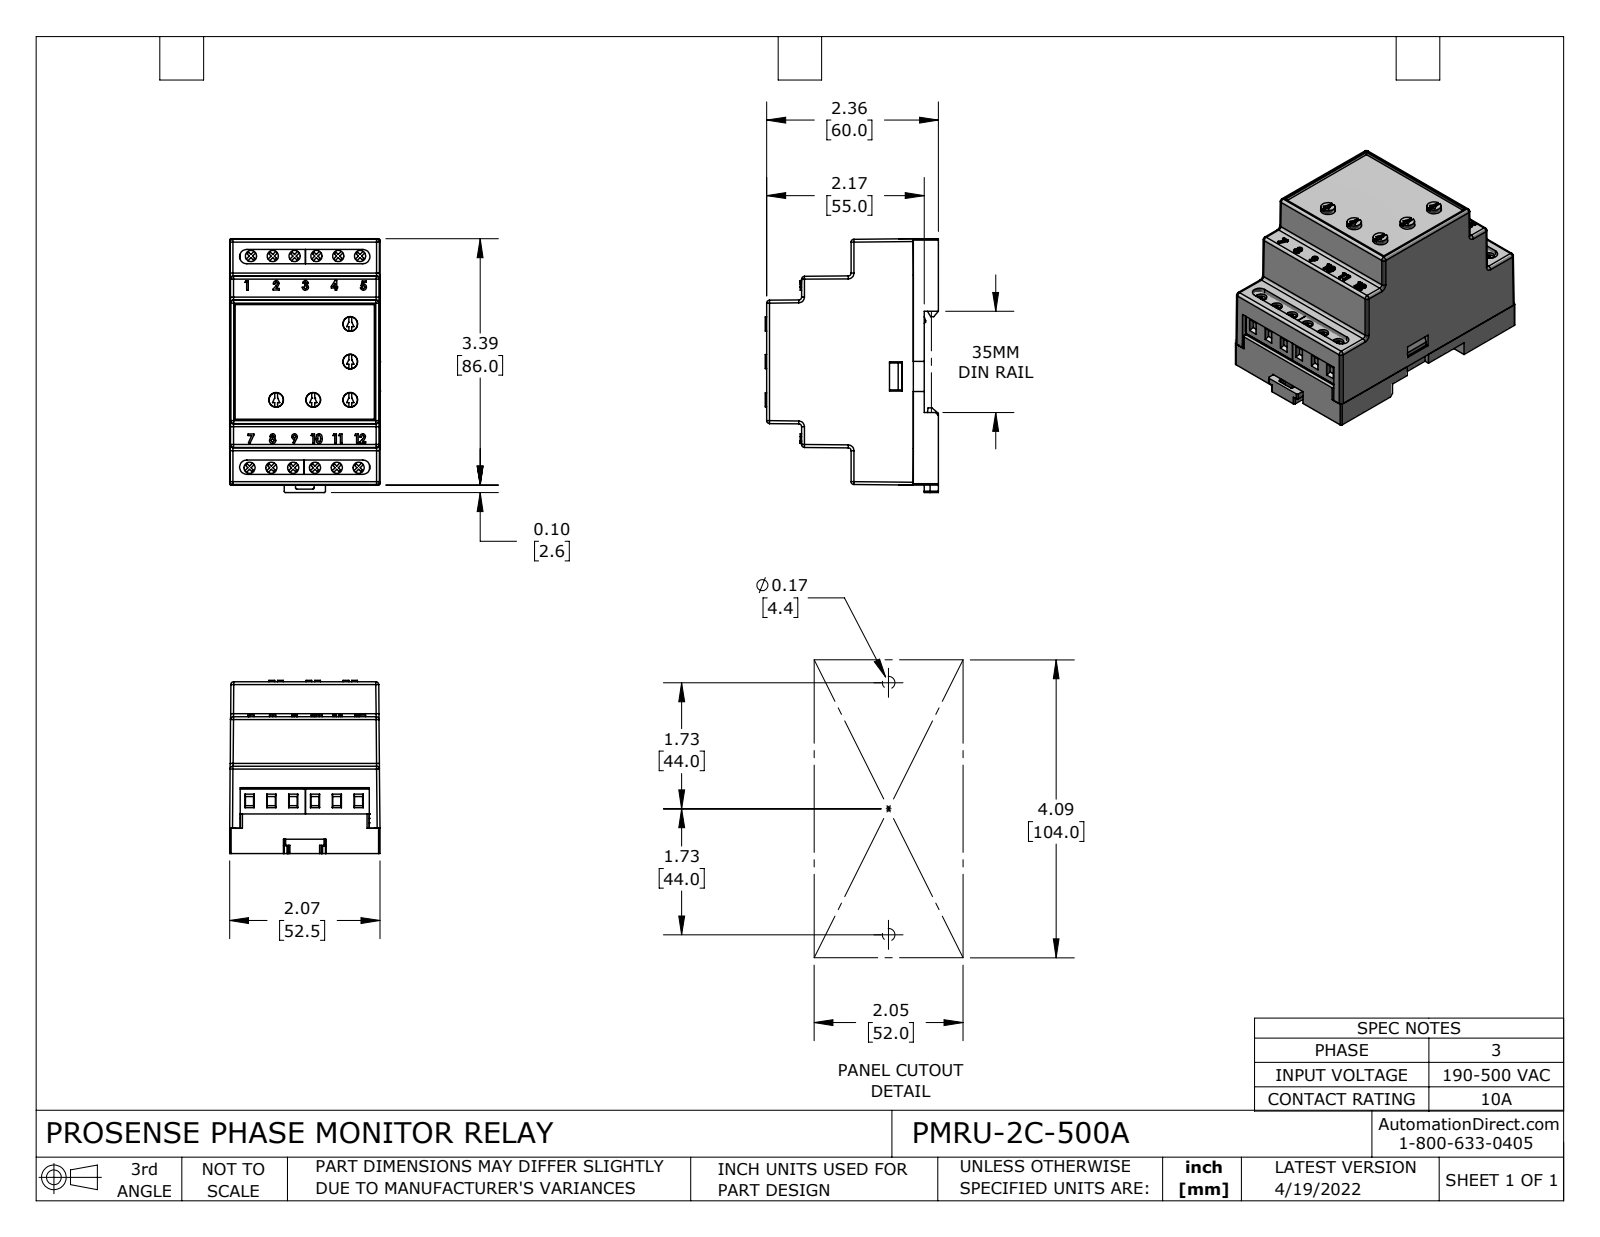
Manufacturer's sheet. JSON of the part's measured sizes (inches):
{"part_name": "PMRU-2C-500A", "step_written_by": "SolidWorks 2021 (CONFIG_CONTROL_DESIGN)", "units": "inches", "bodies": {"solids": 13, "faces": 1220, "planar": 891, "cylindrical": 206, "other": 123}, "overall_size": [3.489, 2.382, 2.067], "volume_in3": 3.469, "surface_area_in2": 99.03, "round_holes": [[0.154, 12], [0.203, 5]], "round_bosses_or_shafts": [[0.197, 5], [0.148, 2], [0.091, 1], [0.087, 1]], "partial_cylinders_radius": [[0.01, 40], [0.02, 36], [0.039, 28], [0.021, 16], [0.02, 4], [0.03, 4], [0.098, 4], [0.01, 2]], "face_to_face_distances": [0.059, 0.285, 0.062, 0.347, 0.094, 0.191, 0.253, 2.067, 0.079, 2.126], "hole_center_spacings": [0.3, 0.6, 0.9, 2.909, 2.923, 2.927, 1.2, 2.967]}
